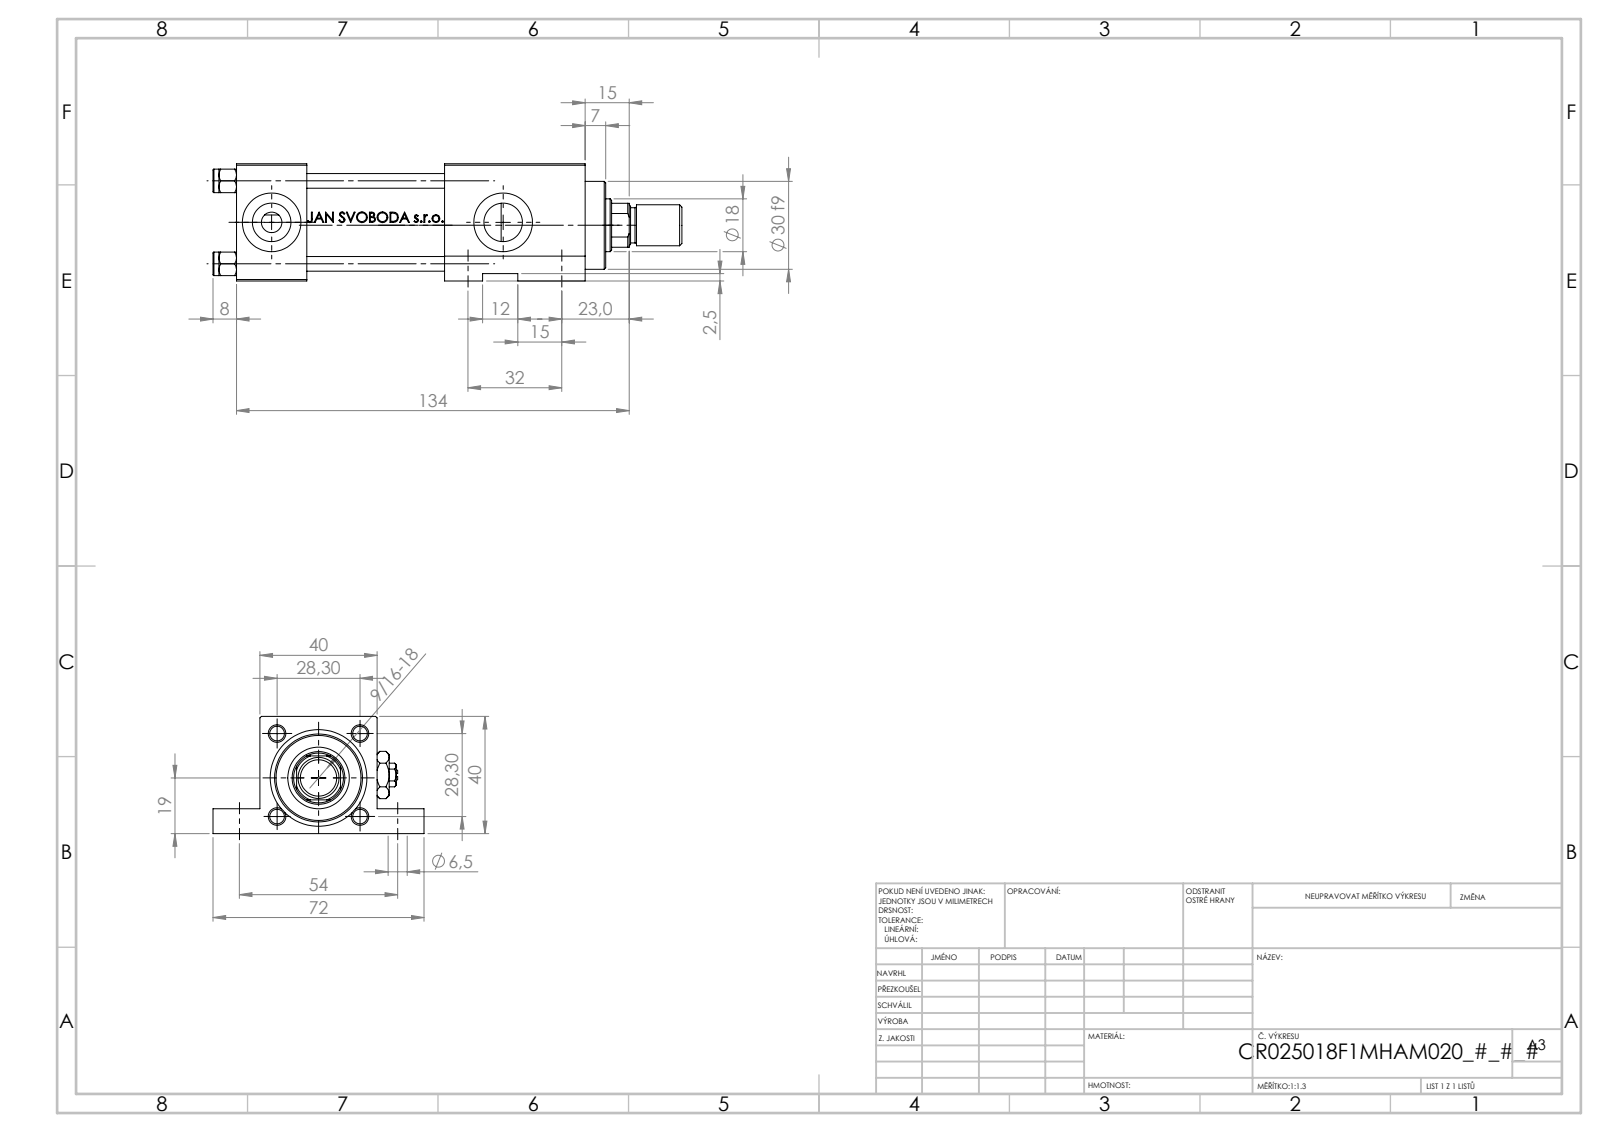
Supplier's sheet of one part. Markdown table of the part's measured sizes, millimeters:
| quantity | value |
| --- | --- |
| part name | V215CR_VCP_F; ROD_END_AH; V215CR_F_TYCINKA; Zatka_pro_OIL_PORT (+3 more) |
| STEP written by | SolidWorks 2019 (CONFIG_CONTROL_DESIGN) |
| units | millimeters |
| bodies | 13 solids, 1161 faces (463 planar, 132 cylindrical, 566 other) |
| overall size | 160 × 72 × 40 |
| volume | 162 143 mm³ |
| surface area | 62 590 mm² |
| round holes (diameter × count) | 5 × 4, 6.5 × 4, 20 × 4, 13.16 × 3, 7 × 2, 8.5 × 1, 18 × 1, 21 × 1, 25 × 1, 30 × 1 |
| round bosses / shafts (diameter × count) | 8 × 4, 31 × 1, 14 × 1, 12 × 1 |
| partial cylindrical surfaces (radius × count) | 8.5 × 1 |
| main face-to-face distances | 40, 24, 8.5, 31.5, 47, 71, 6, 48, 56, 119 |
| hole center spacings | 28.3, 19.32, 20.73, 32, 40.02, 54, 62.77, 7 |
